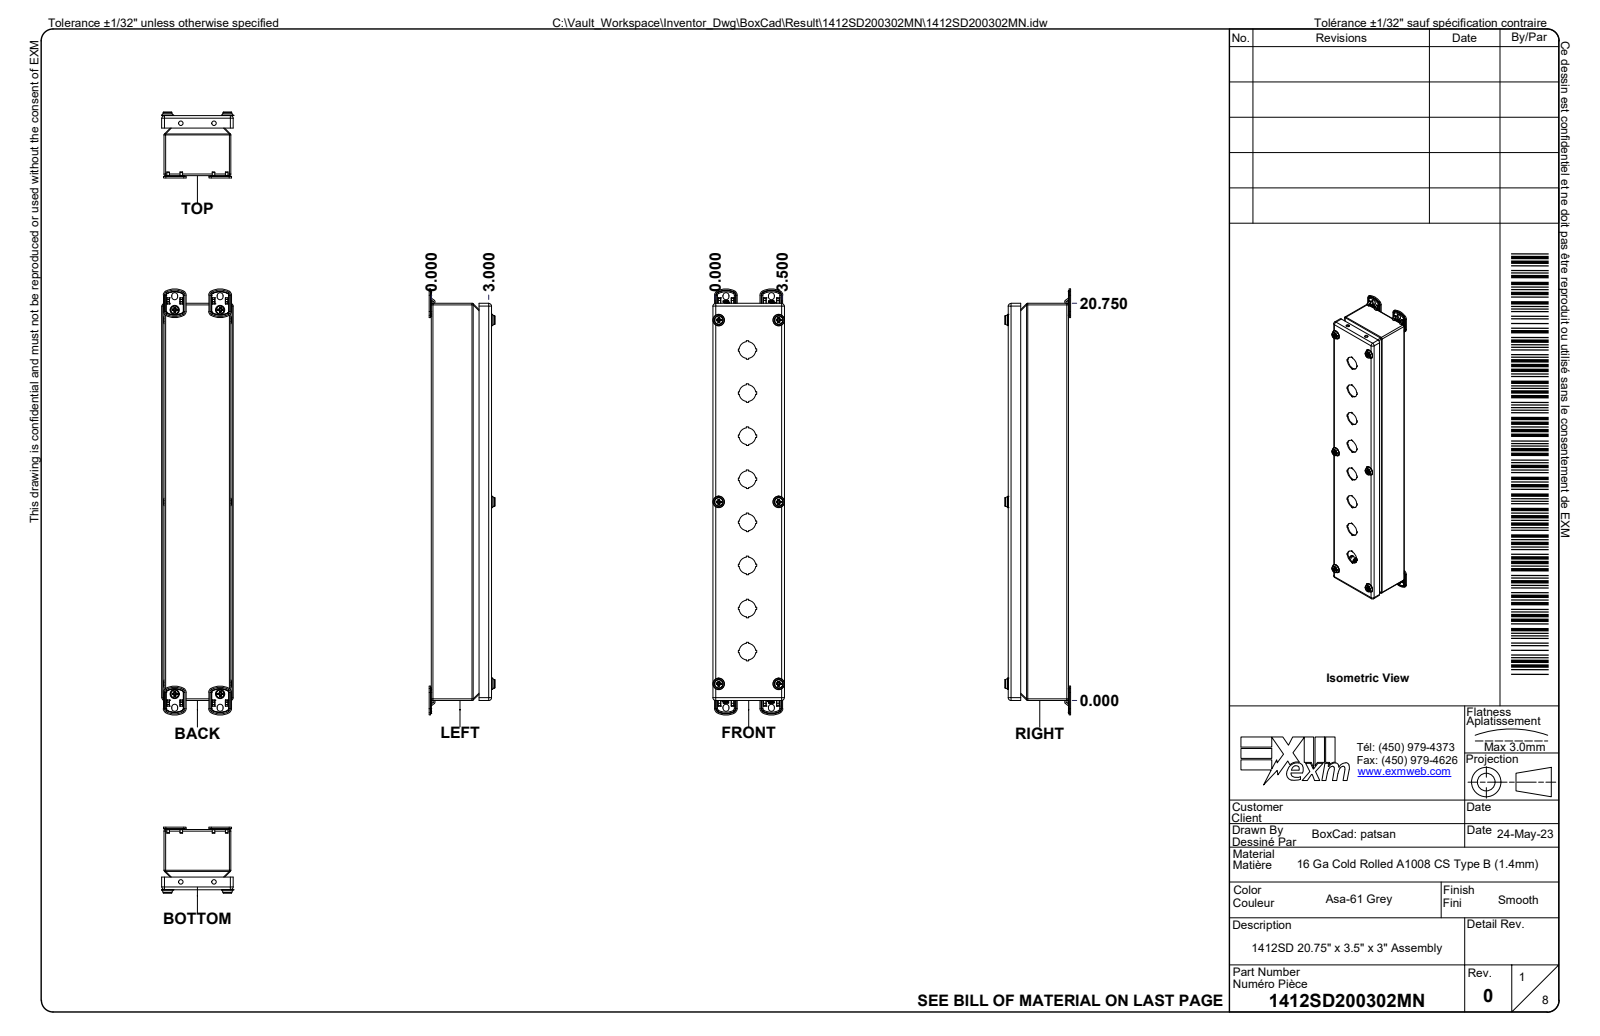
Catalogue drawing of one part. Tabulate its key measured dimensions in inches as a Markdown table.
| quantity | value |
| --- | --- |
| part name | 1412SD200302MN; 1412SD200302MNB; 1412SD200302MNB-P; RIVET_NUT_M5_FH_OE (+8 more) |
| STEP written by | Autodesk Inventor 2024 (AUTOMOTIVE_DESIGN) |
| units | inches |
| bodies | 35 solids, 3690 faces (1002 planar, 1260 cylindrical, 1428 other) |
| overall size | 22.246 × 3.736 × 3.441 |
| volume | 20.54 in³ |
| surface area | 745.5 in² |
| round holes (diameter × count) | 0.875 × 8, 0.157 × 6, 0.198 × 6, 0.277 × 6, 0.197 × 4, 0.03 × 2, 0.201 × 2, 0.23 × 2, 0.24 × 2 |
| round bosses / shafts (diameter × count) | 0.591 × 6, 0.277 × 6, 0.193 × 6, 0.138 × 6, 0.5 × 4, 0.232 × 4, 0.394 × 2, 0.035 × 2 |
| partial cylindrical surfaces (radius × count) | 0.008 × 292, 0.004 × 100, 0.01 × 60, 0.039 × 41, 0.012 × 36, 0.031 × 28, 0.047 × 28, 0.236 × 28 |
| main face-to-face distances | 0.053, 0.053, 3.447, 3.092, 3.039, 3.145, 3.092, 0.118, 3.5, 3.394 |
| hole center spacings | 2.25, 4.5, 6.75, 0.652, 2.804, 9, 9.5, 10.003 |
